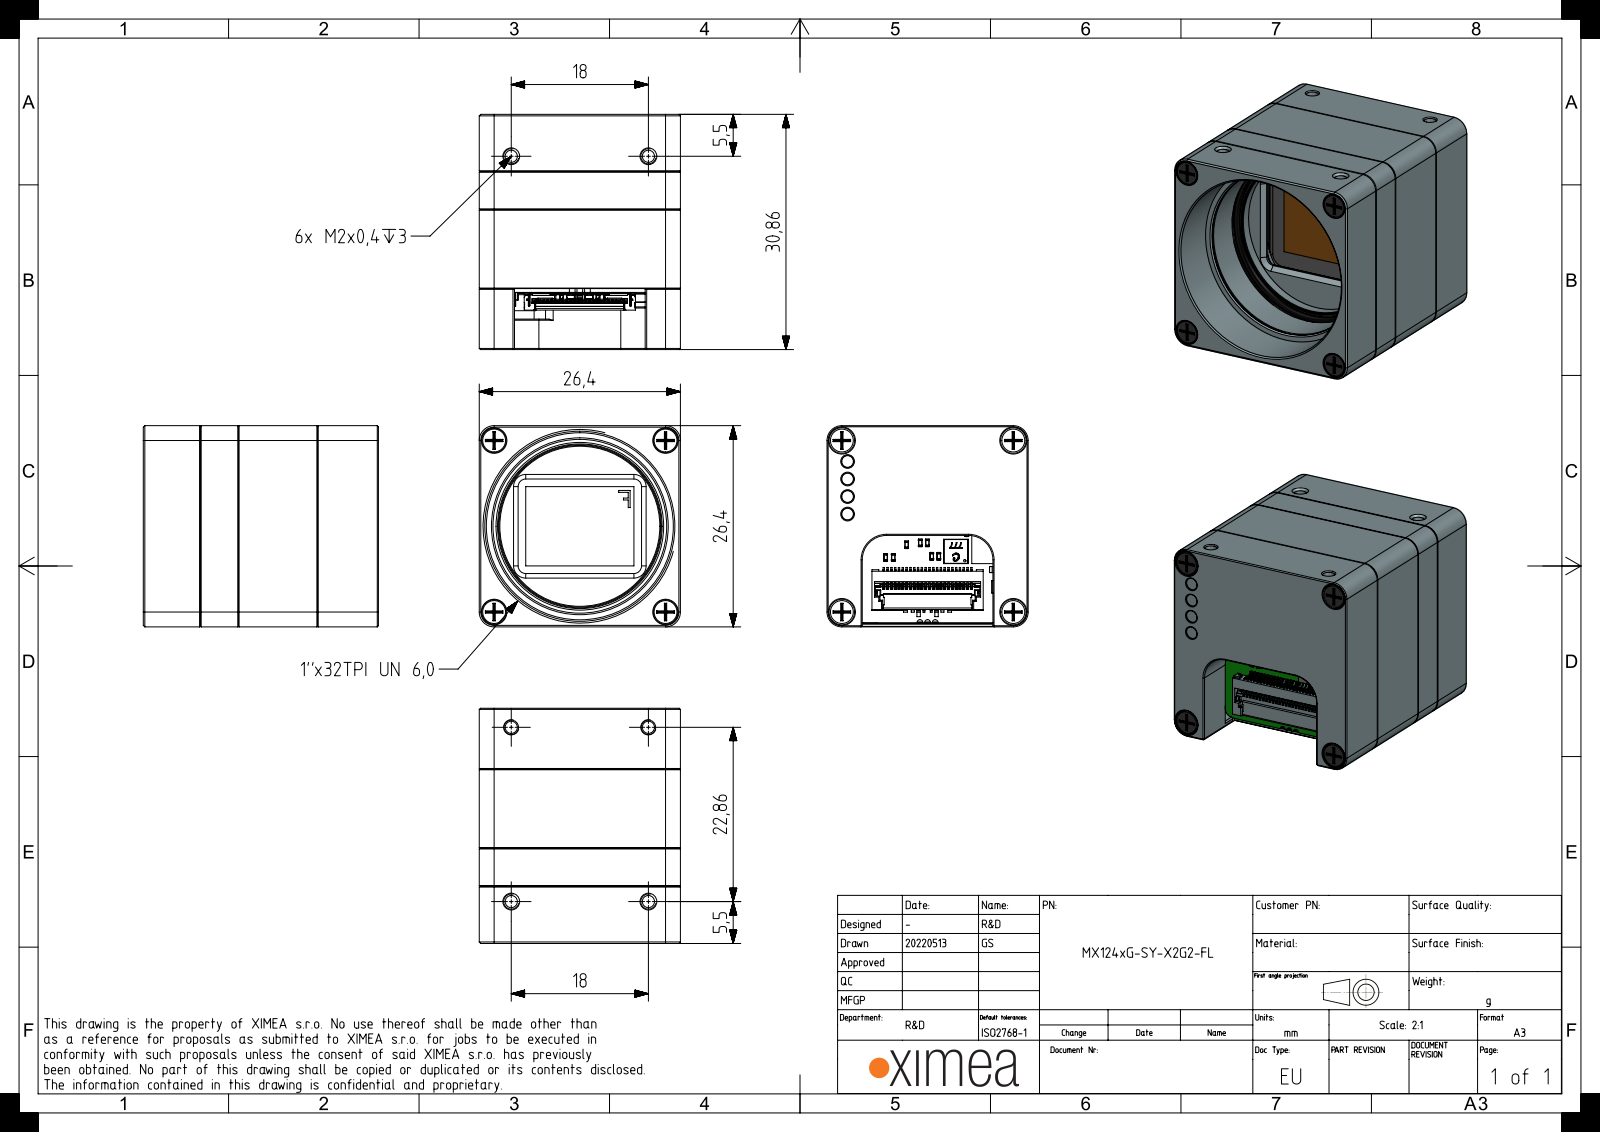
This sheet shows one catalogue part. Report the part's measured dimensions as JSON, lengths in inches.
{"part_name": "MT124xG-PR-SENSOR-PCA; MECH-O-RING-22X1-VI370; FLT-BK7-AR2X-D25; SROB-M1.6x3-SLOT-STNLS (+8 more)", "step_written_by": "SIEMENS PLM Software NX 1907 (AUTOMOTIVE_DESIGN)", "units": "inches", "bodies": {"solids": 31, "faces": 7564, "planar": 5196, "cylindrical": 2093, "other": 275}, "overall_size": [1.215, 1.039, 1.039], "volume_in3": 0.628, "surface_area_in2": 26.8, "round_holes": [[0.063, 12], [0.035, 4], [0.079, 4], [0.083, 4], [0.118, 4], [0.126, 4], [0.132, 4], [0.051, 2], [0.067, 2], [0.827, 1], [0.898, 1], [0.961, 1]], "round_bosses_or_shafts": [[0.075, 4], [0.064, 4], [0.033, 4], [0.118, 2], [0.063, 2], [0.984, 1], [0.85, 1]], "partial_cylinders_radius": [[0.013, 17], [0.059, 15], [0.004, 14], [0.006, 14], [0.039, 14], [0.015, 12], [0.008, 10], [0.01, 8]], "face_to_face_distances": [0.039, 1.039, 0.142, 0.451, 0.27, 0.1, 0.181, 0.412, 0.408, 0.266], "hole_center_spacings": [0.626, 0.886, 0.091, 0.148, 0.181, 0.531, 0.709, 0.738]}
